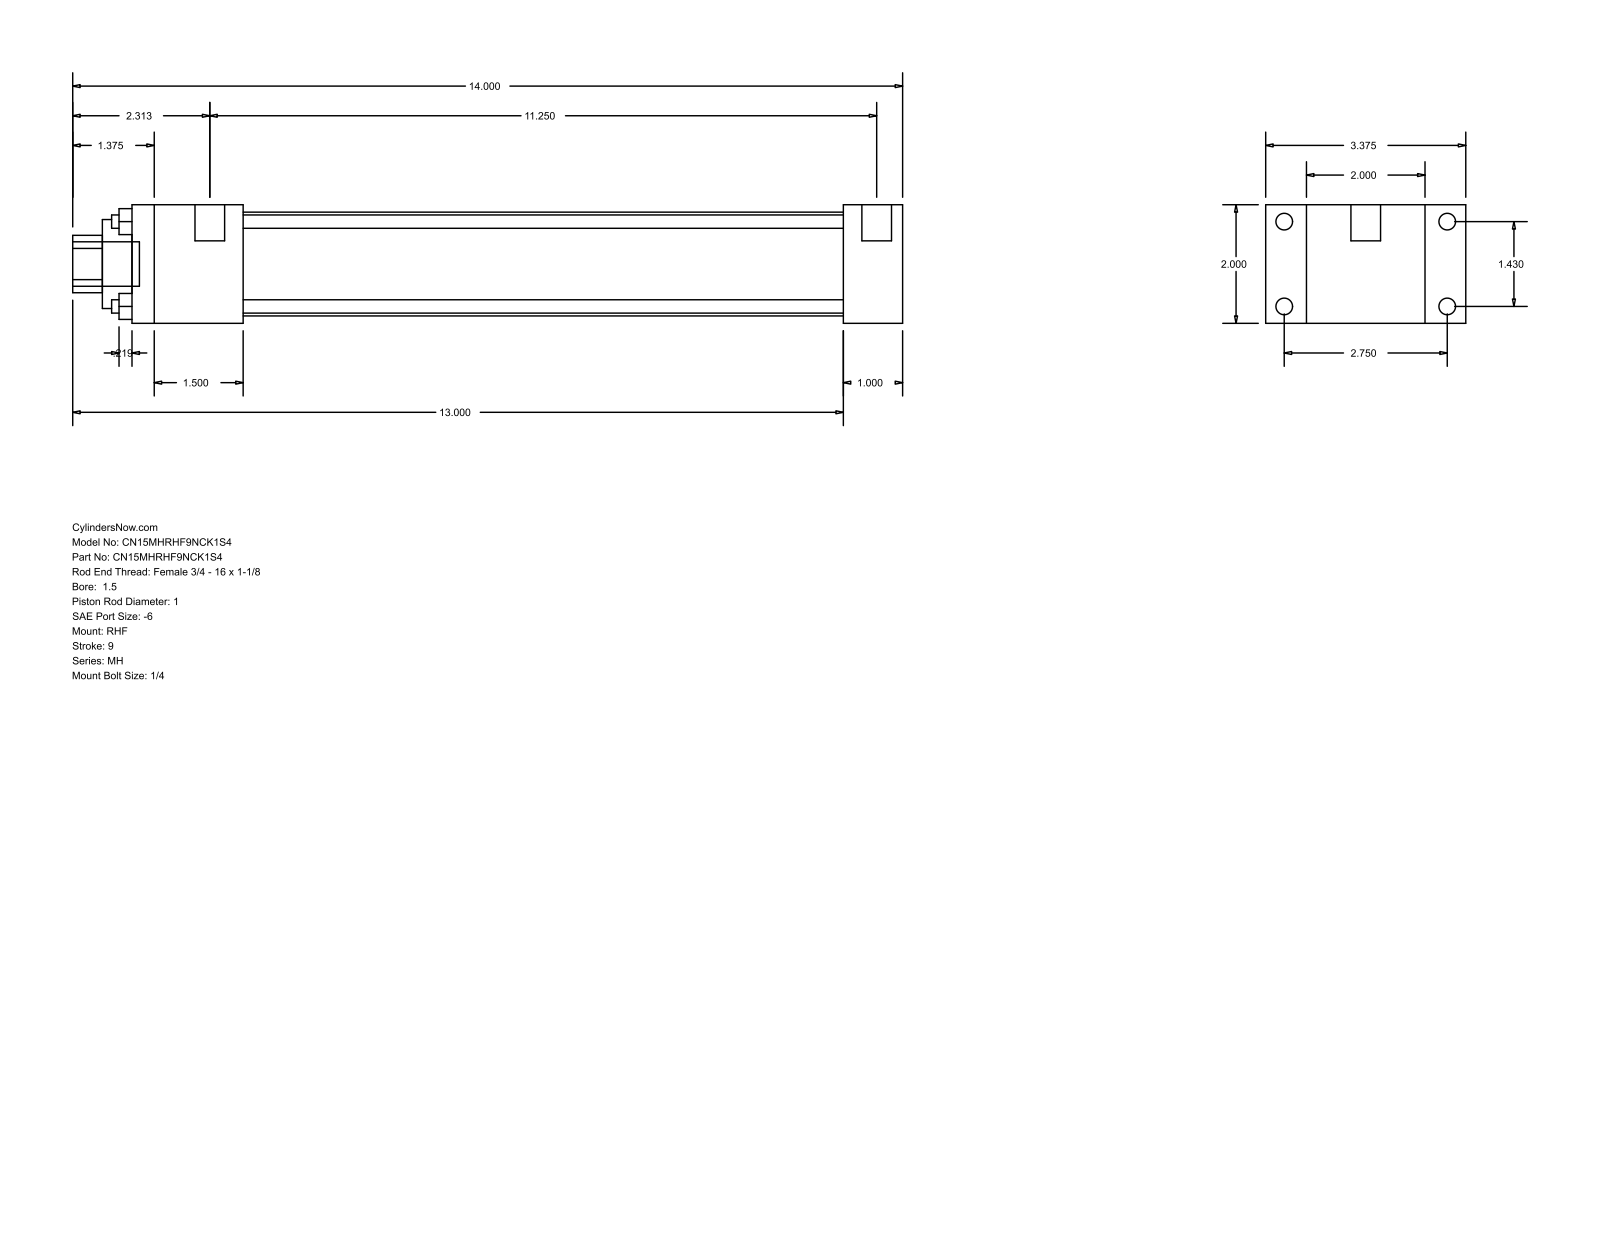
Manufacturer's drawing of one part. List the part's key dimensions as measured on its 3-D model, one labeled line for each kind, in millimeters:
Part name (STEP PRODUCT): MH_RHF__0150_1
STEP written by: GSSL Pune (CONFIG_CONTROL_DESIGN)
Units: millimetres
Bodies: 0 solids, 88 faces (60 planar, 28 cylindrical, 0 other)
Overall size (bounding box): 355.6 × 85.72 × 50.8
Round holes (diameter × count): ⌀5.71 ×4, ⌀25.4 ×1, ⌀38.1 ×1, ⌀44.45 ×1
Round bosses / shafts (diameter × count): ⌀7.14 ×4, ⌀5.56 ×4, ⌀12.7 ×2, ⌀19.05 ×1
Partial cylindrical surfaces — rounded edges, fillets, slot ends (radius × count): R12.29 ×1
Main face-to-face distances: 50.8, 25.4, 17.46, 68.26, 85.72, 330.2, 304.8, 47.63, 257.17, 282.57
Hole centre spacings: 25.68, 36.32, 51.36
